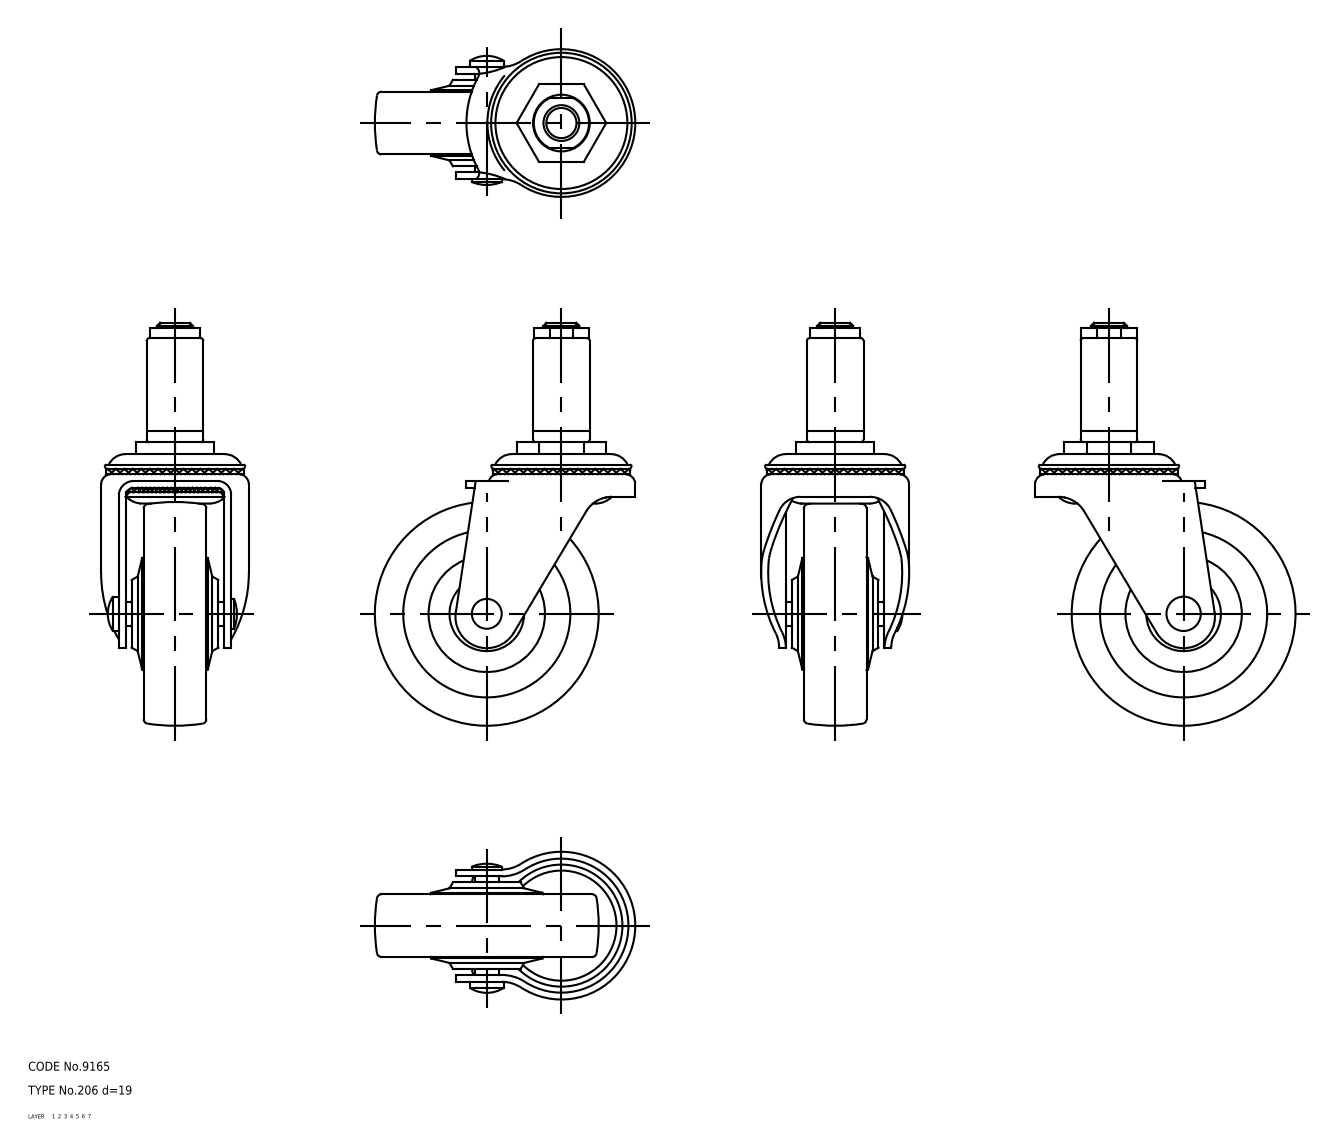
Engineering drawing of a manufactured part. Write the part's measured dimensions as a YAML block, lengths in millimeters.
part_name: "wheel; main shaft; axle; No_206_d19_5961_36"
step_written_by: "CADfix (AUTOMOTIVE_DESIGN)"
units: millimeters
bodies: {solids: 4, faces: 175, planar: 0, cylindrical: 0, other: 175}
overall_size: [135, 87.25, 49.5]
volume: 139178
surface_area: 34152
